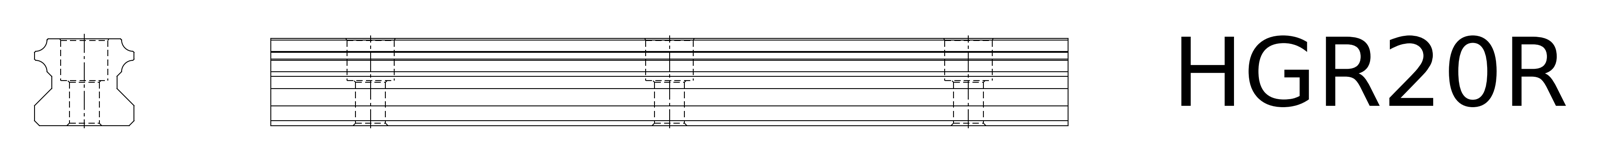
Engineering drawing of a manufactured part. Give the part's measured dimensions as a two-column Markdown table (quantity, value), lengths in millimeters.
| quantity | value |
| --- | --- |
| part name | HGR20R |
| STEP written by | SolidWorks 2006104 (CONFIG_CONTROL_DESIGN) |
| units | millimeters |
| bodies | 1 solid, 59 faces (25 planar, 34 cylindrical, 0 other) |
| overall size | 150 × 20 × 17.5 |
| volume | 42 265 mm³ |
| surface area | 13 187 mm² |
| round holes (diameter × count) | 6 × 3, 9.5 × 3 |
| partial cylindrical surfaces (radius × count) | 0.5 × 12, 1 × 6, 2.03 × 4 |
| main face-to-face distances | 17.5, 20, 3.4, 16.6, 16.32, 8.67, 7.65, 150, 23.85, 15.18 |
| hole center spacings | 60, 120 |
